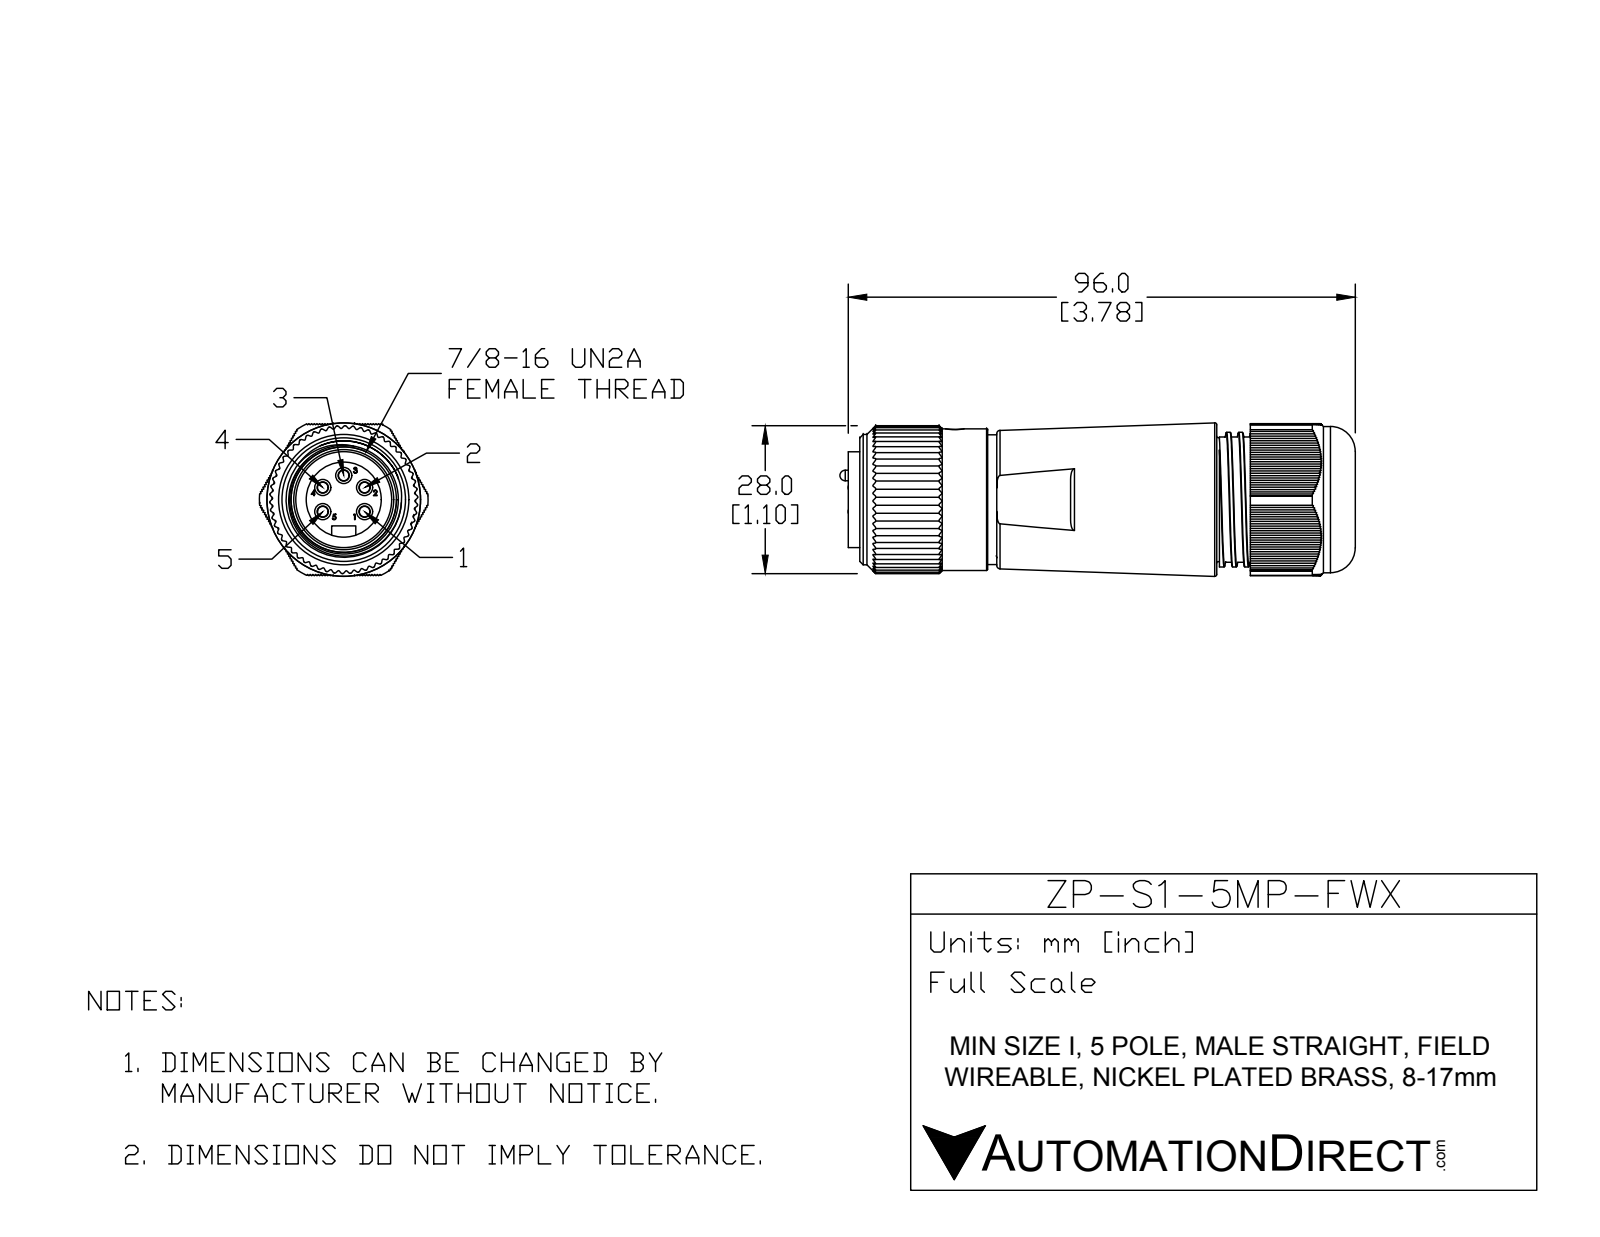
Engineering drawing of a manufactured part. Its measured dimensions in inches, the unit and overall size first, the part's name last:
Units: inches
Overall size (bounding box): 3.841 × 1.256 × 1.144
Round holes (diameter × count): ⌀0.14 ×1, ⌀0.56 ×1, ⌀0.68 ×1, ⌀0.81 ×1, ⌀0.849 ×1, ⌀0.953 ×1, ⌀1 ×1
Round bosses / shafts (diameter × count): ⌀0.124 ×5, ⌀0.079 ×5, ⌀1.09 ×1, ⌀1.055 ×1, ⌀1.004 ×1, ⌀0.972 ×1, ⌀0.957 ×1, ⌀0.714 ×1
Partial cylindrical surfaces — rounded edges, fillets, slot ends (radius × count): R0.01 ×165, R0.09 ×1, R0.551 ×1, R0.628 ×1
Main face-to-face distances: 2.701, 0.042, 0.014, 0.028, 0.056, 0.083, 0.07, 0.346, 2.355, 0.808
Volume: 3.03 in³ · Surface area: 26.46 in²
Bodies: 9 solids, 913 faces (521 planar, 314 cylindrical, 78 other)
Part name (STEP PRODUCT): ZP-S1-5MP-FWX
STEP written by: SolidWorks 2015 (AUTOMOTIVE_DESIGN)
